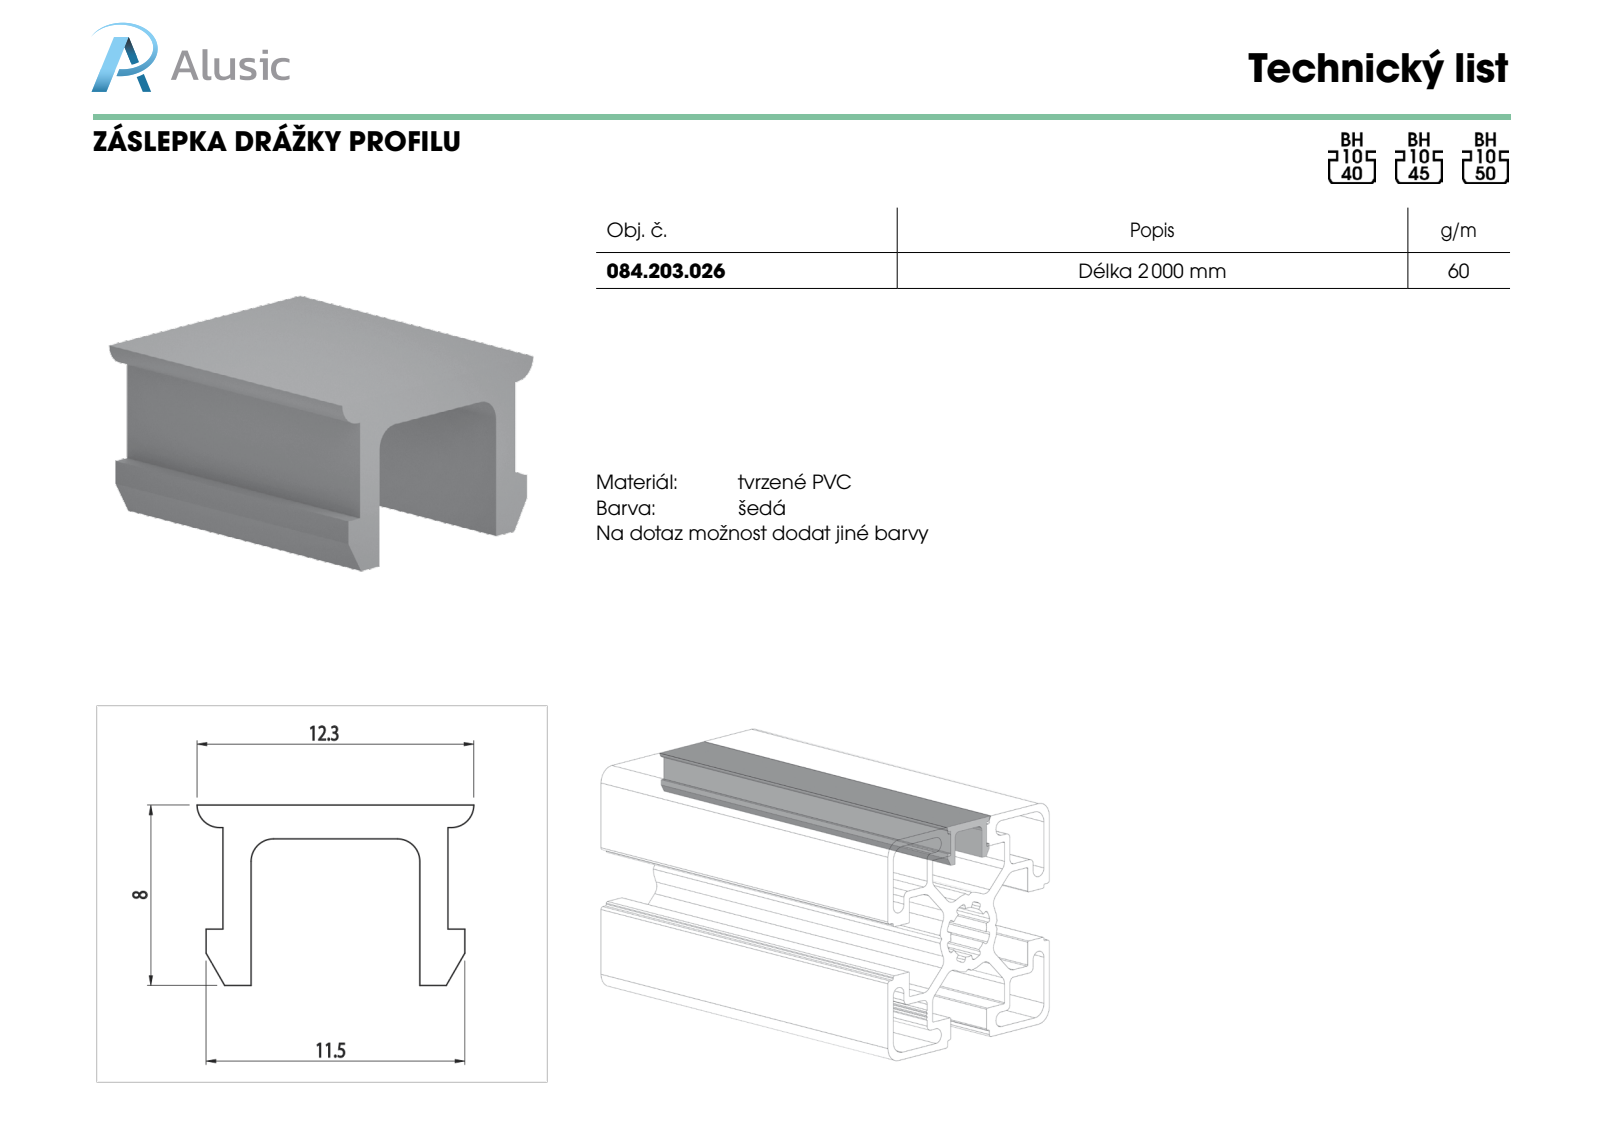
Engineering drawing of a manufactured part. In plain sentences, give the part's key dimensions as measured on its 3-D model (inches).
The part is named "084.203.026". Its 3-D file was written by "SolidWorks 2016 (CONFIG_CONTROL_DESIGN)". It is 1 solid with 22 faces: 18 planar, 4 cylindrical and 0 other. Overall it measures 3.937 by 0.484 by 0.315 inches. Its volume is 0.22 cubic inches and its surface area 8.43 square inches. Partial cylindrical surfaces (rounded edges, fillets, slot ends): 4 of radius 0.039. The main face-to-face distances are 0.049, 0.344, 0.295, 0.059, 0.394, 0.256, 0.315, 0.03, 0.079, 0.374.
